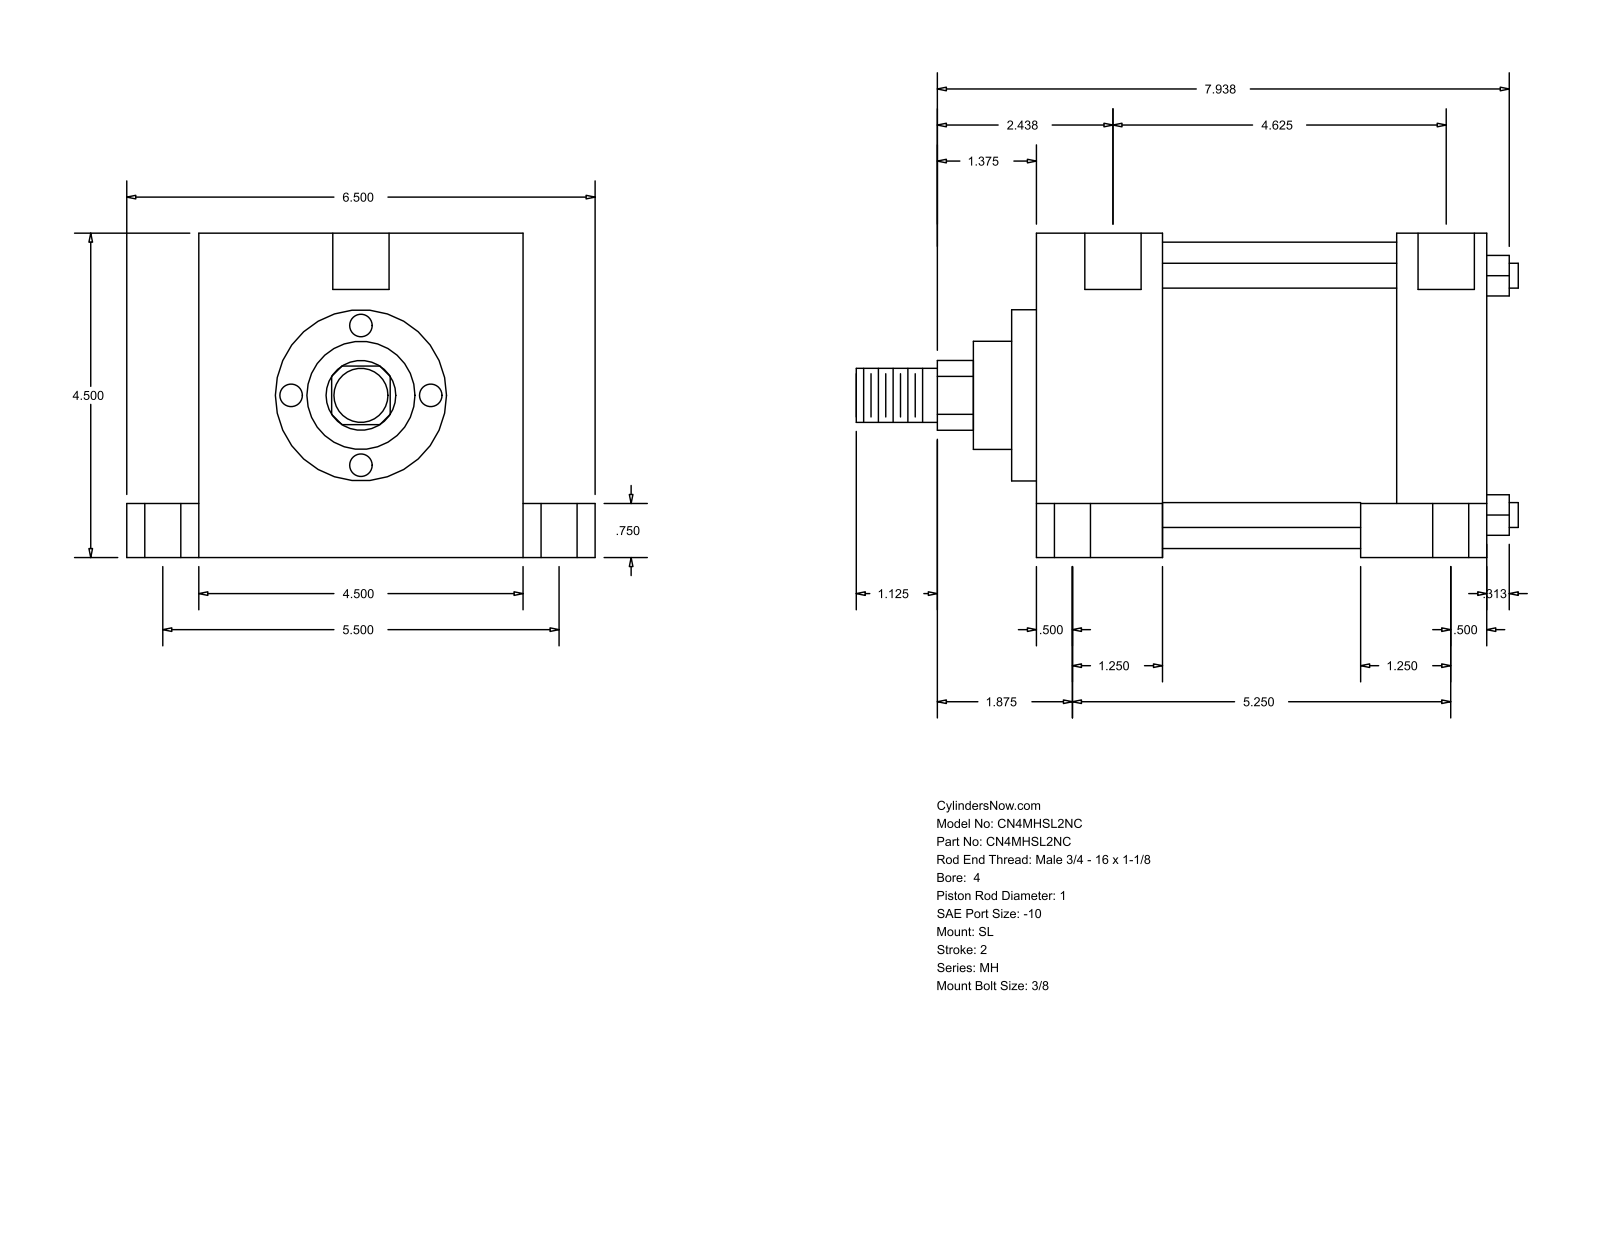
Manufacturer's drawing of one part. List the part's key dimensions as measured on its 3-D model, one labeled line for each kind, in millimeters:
Part name (STEP PRODUCT): MH_SL__0400_1
STEP written by: GSSL Pune (CONFIG_CONTROL_DESIGN)
Units: millimetres
Bodies: 0 solids, 110 faces (77 planar, 33 cylindrical, 0 other)
Overall size (bounding box): 233.36 × 165.1 × 114.3
Round holes (diameter × count): ⌀8.73 ×4, ⌀12.7 ×4, ⌀19.05 ×4, ⌀19.84 ×2
Round bosses / shafts (diameter × count): ⌀8.76 ×4, ⌀107.95 ×1, ⌀60.33 ×1, ⌀38.1 ×1, ⌀25.4 ×1, ⌀19.05 ×1
Partial cylindrical surfaces — rounded edges, fillets, slot ends (radius × count): R12.29 ×1
Main face-to-face distances: 114.3, 158.76, 44.46, 127.01, 82.55, 31.75, 25.4, 139.7, 19.05, 95.25
Hole centre spacings: 1.58, 69.85, 69.87, 71, 71.3, 119.06, 120.64, 133.35
